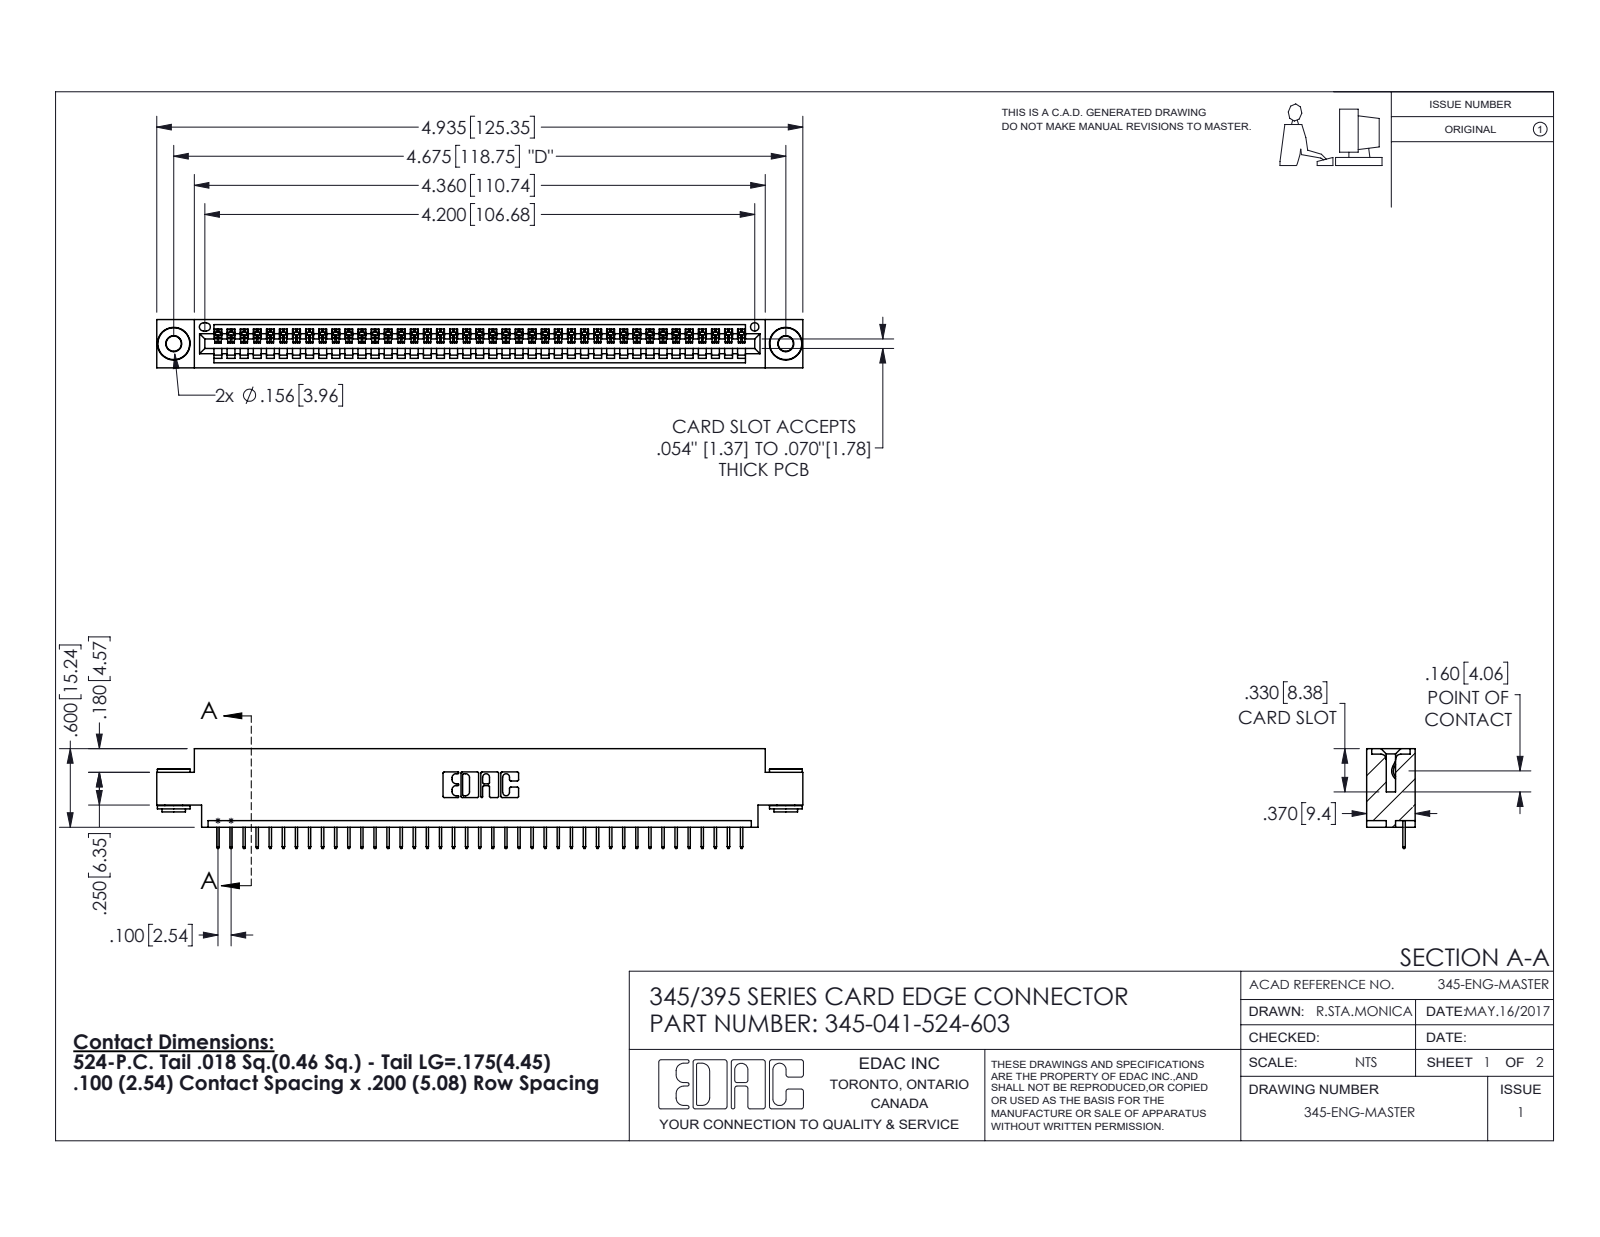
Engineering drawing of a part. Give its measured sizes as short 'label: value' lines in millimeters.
name: 345-292-001_345-293-124; 345-250-002_345-250-002-102; 345-041-524-603; 345 Part_0.170 Offset - 0.156 Dia-TH
written by: SolidWorks 2016 (CONFIG_CONTROL_DESIGN)
unit: mm
bodies: 44 solids, 2710 faces (1980 planar, 722 cylindrical, 8 other)
size: 125.3 × 19.4 × 9.4
volume: 11 600 mm³; area: 15 280 mm²
holes: 2× ⌀2.9, 2× ⌀4, 1× ⌀1.6
bosses: 2× ⌀6.4, 2× ⌀4.6, 2× ⌀3.5
rounds: 82× R0.2, 22× R0.3, 6× R0.2, 6× R0.8, 3× R0.7, 2× R0.8, 2× R1, 1× R0.4
face distances: 1.8, 7.6, 9.4, 5.1, 2.5, 6.9, 0.6, 5.7, 4.4, 1.8
hole spacings: 6.9, 112.8, 118.7
